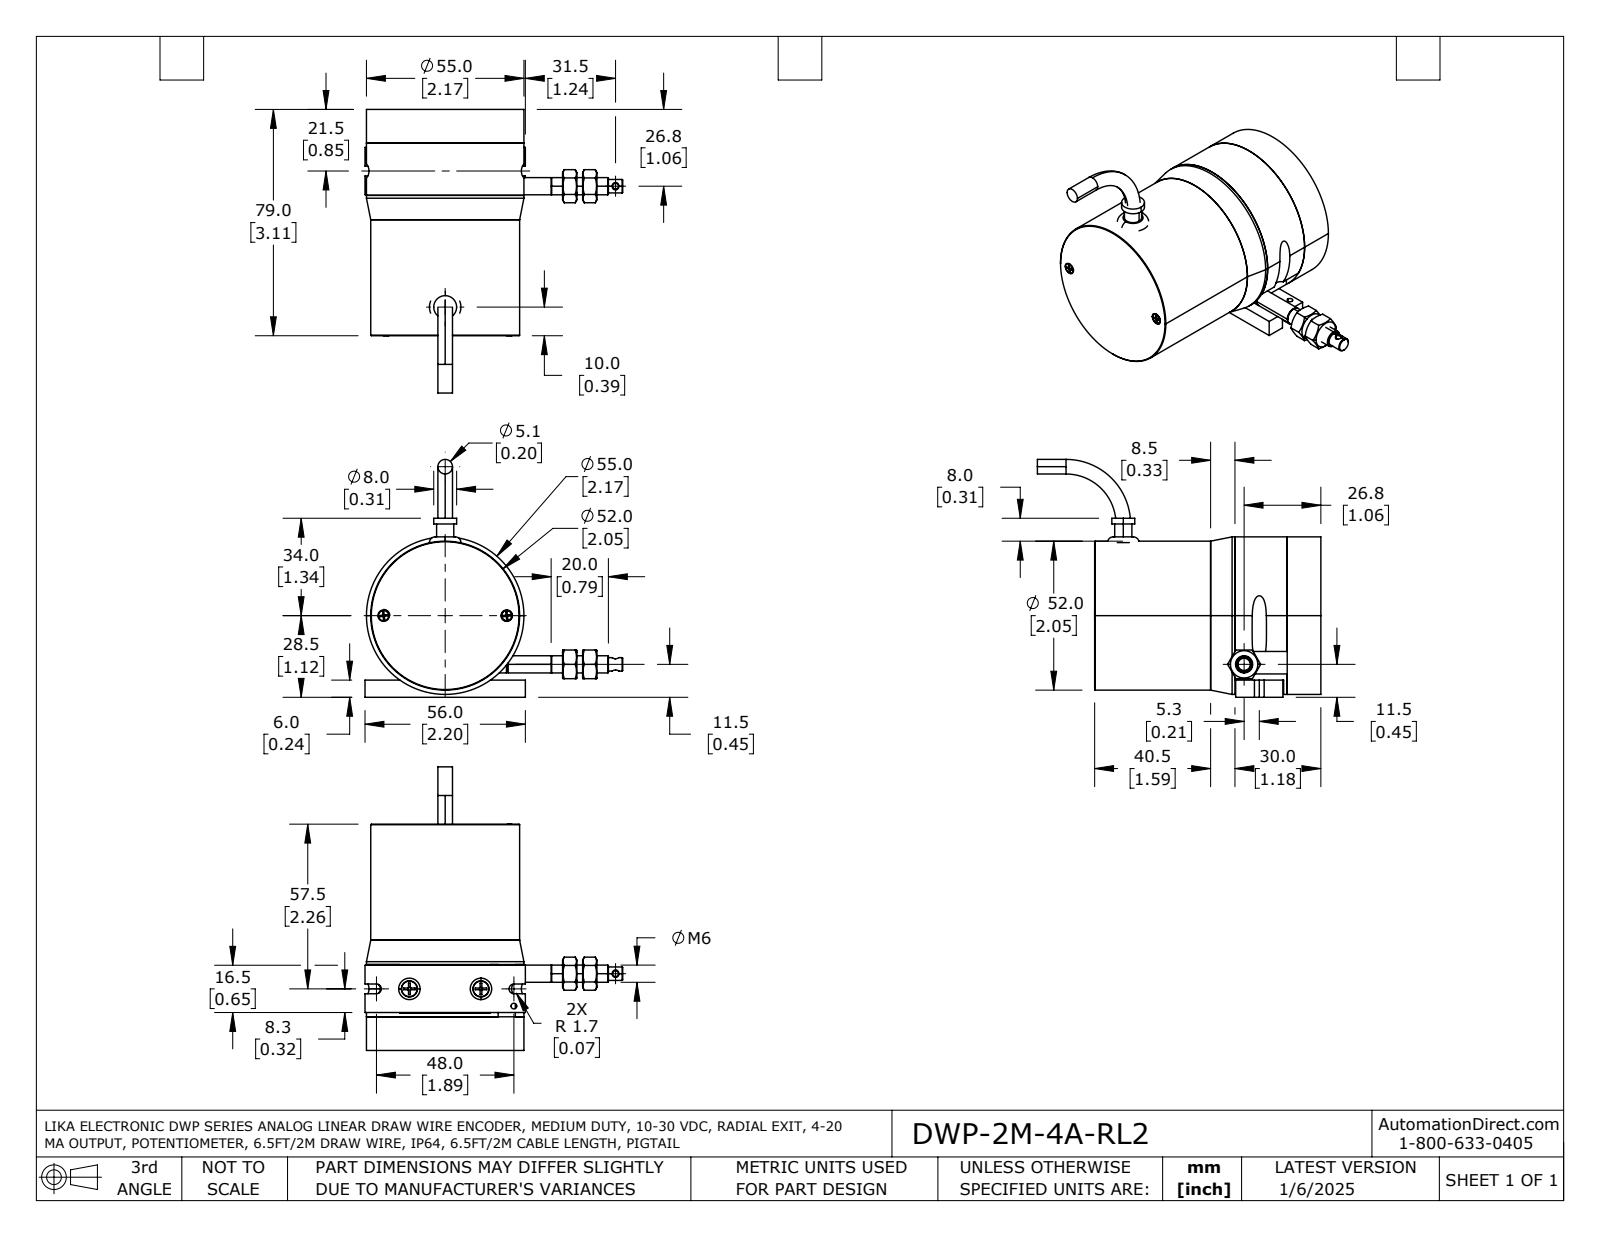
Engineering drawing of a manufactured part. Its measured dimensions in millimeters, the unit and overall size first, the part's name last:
Units: millimetres
Overall size (bounding box): 99 × 90 × 83.1
Round holes (diameter × count): ⌀1.6 ×8, ⌀5 ×7, ⌀2 ×5, ⌀2.1 ×4, ⌀2.1 ×4, ⌀2.8 ×4, ⌀1.5 ×2, ⌀2.2 ×2, ⌀2.5 ×2, ⌀3.4 ×2, ⌀0.8 ×1, ⌀4 ×1
Round bosses / shafts (diameter × count): ⌀3 ×3, ⌀6 ×2, ⌀5.1 ×2, ⌀2.5 ×2, ⌀2 ×2, ⌀55 ×1, ⌀52 ×1, ⌀47.6 ×1
Partial cylindrical surfaces — rounded edges, fillets, slot ends (radius × count): R0.2 ×18, R0.2 ×6, R8 ×5, R2.5 ×3, R1.7 ×2, R5 ×1, R20 ×1, R26.7 ×1
Main face-to-face distances: 2, 77, 30, 79, 49, 47, 9.8, 11.8, 18.3, 65.3
Hole centre spacings: 5, 17, 21.5, 24, 27.4, 29.4, 2.5, 4.5
Volume: 71 200 mm³ · Surface area: 47 460 mm²
Bodies: 20 solids, 588 faces (164 planar, 216 cylindrical, 208 other)
Part name (STEP PRODUCT): DWP-2M-4A-RL2
STEP written by: SolidWorks 2021 (AUTOMOTIVE_DESIGN)
